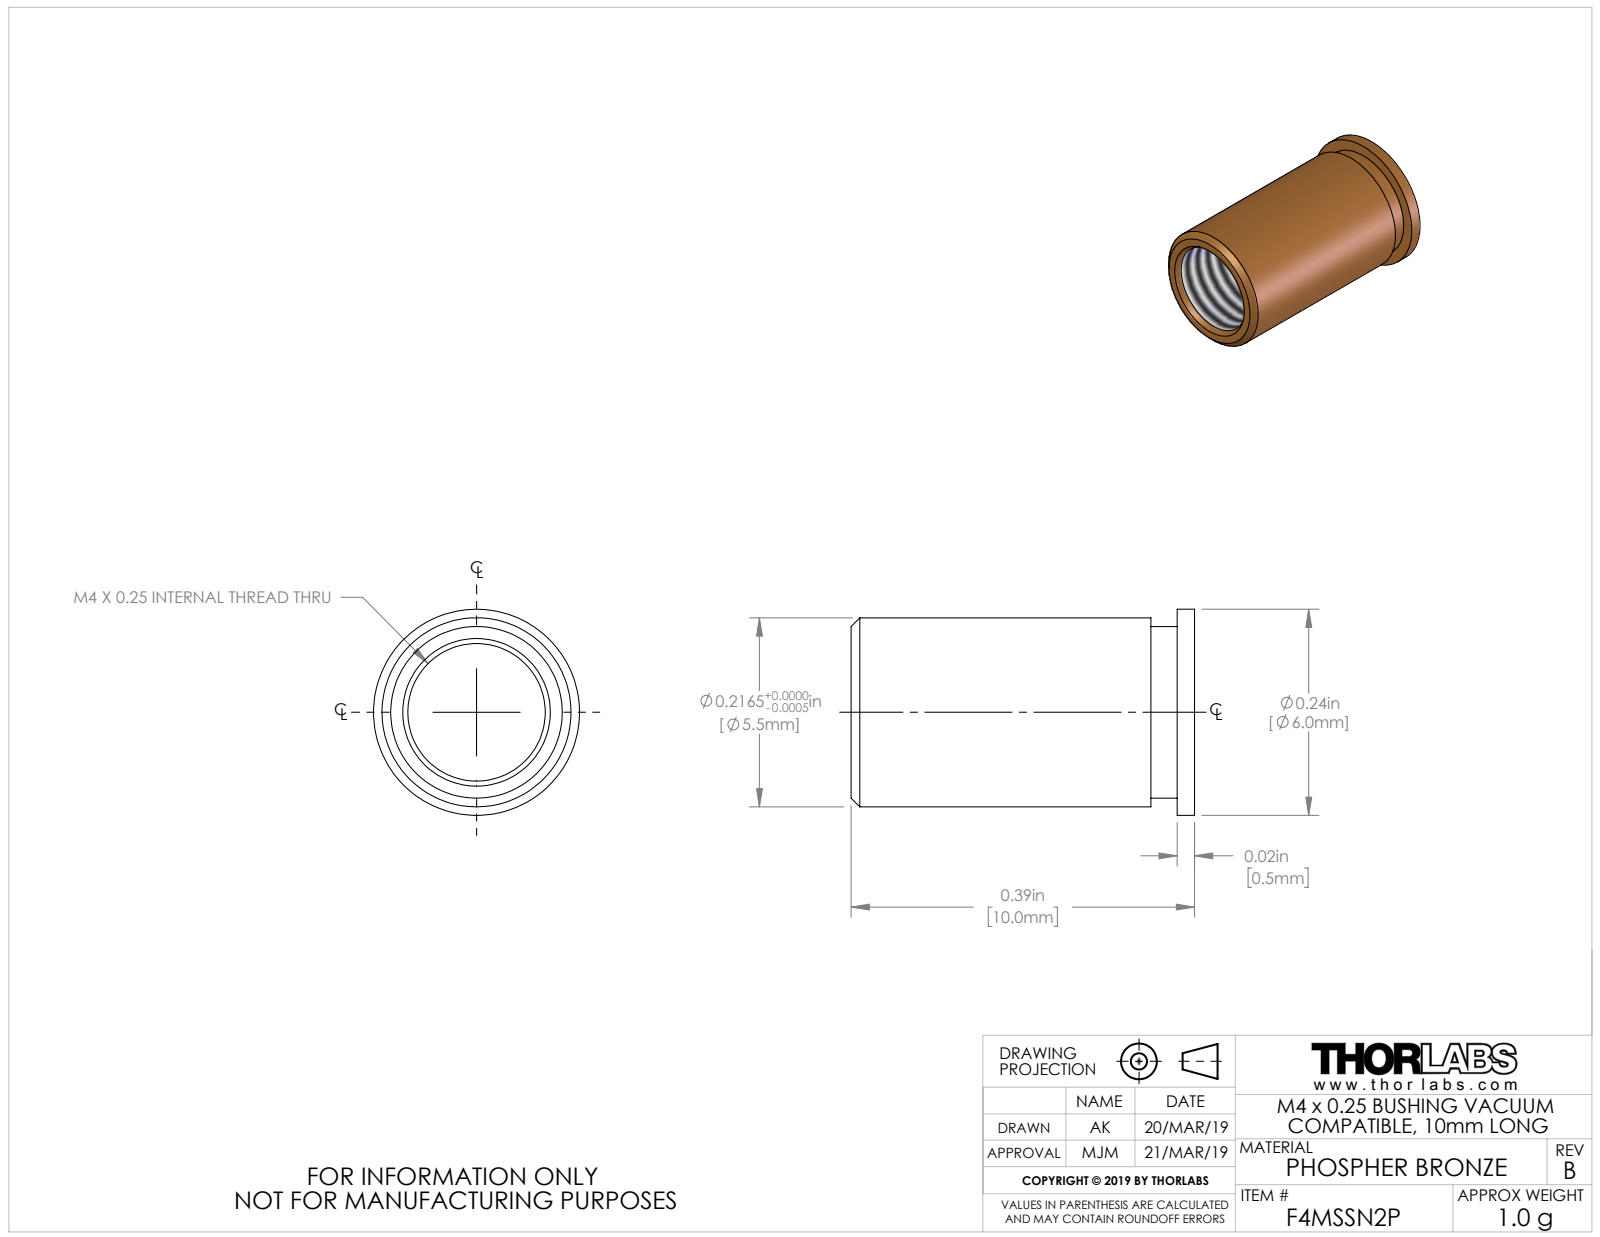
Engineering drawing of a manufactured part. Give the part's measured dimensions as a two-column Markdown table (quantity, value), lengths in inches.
| quantity | value |
| --- | --- |
| part name | TTN182092-E0W |
| STEP written by | SolidWorks 2018 (AUTOMOTIVE_DESIGN) |
| units | inches |
| bodies | 1 solid, 18 faces (4 planar, 8 cylindrical, 6 other) |
| overall size | 0.394 × 0.236 × 0.236 |
| volume | 0.007 in³ |
| surface area | 0.515 in² |
| round holes (diameter × count) | 0.157 × 1 |
| round bosses / shafts (diameter × count) | 0.236 × 1, 0.217 × 1, 0.197 × 1 |
| main face-to-face distances | 0.02, 0.394, 0.374, 0.05, 0.03, 0.344 |
